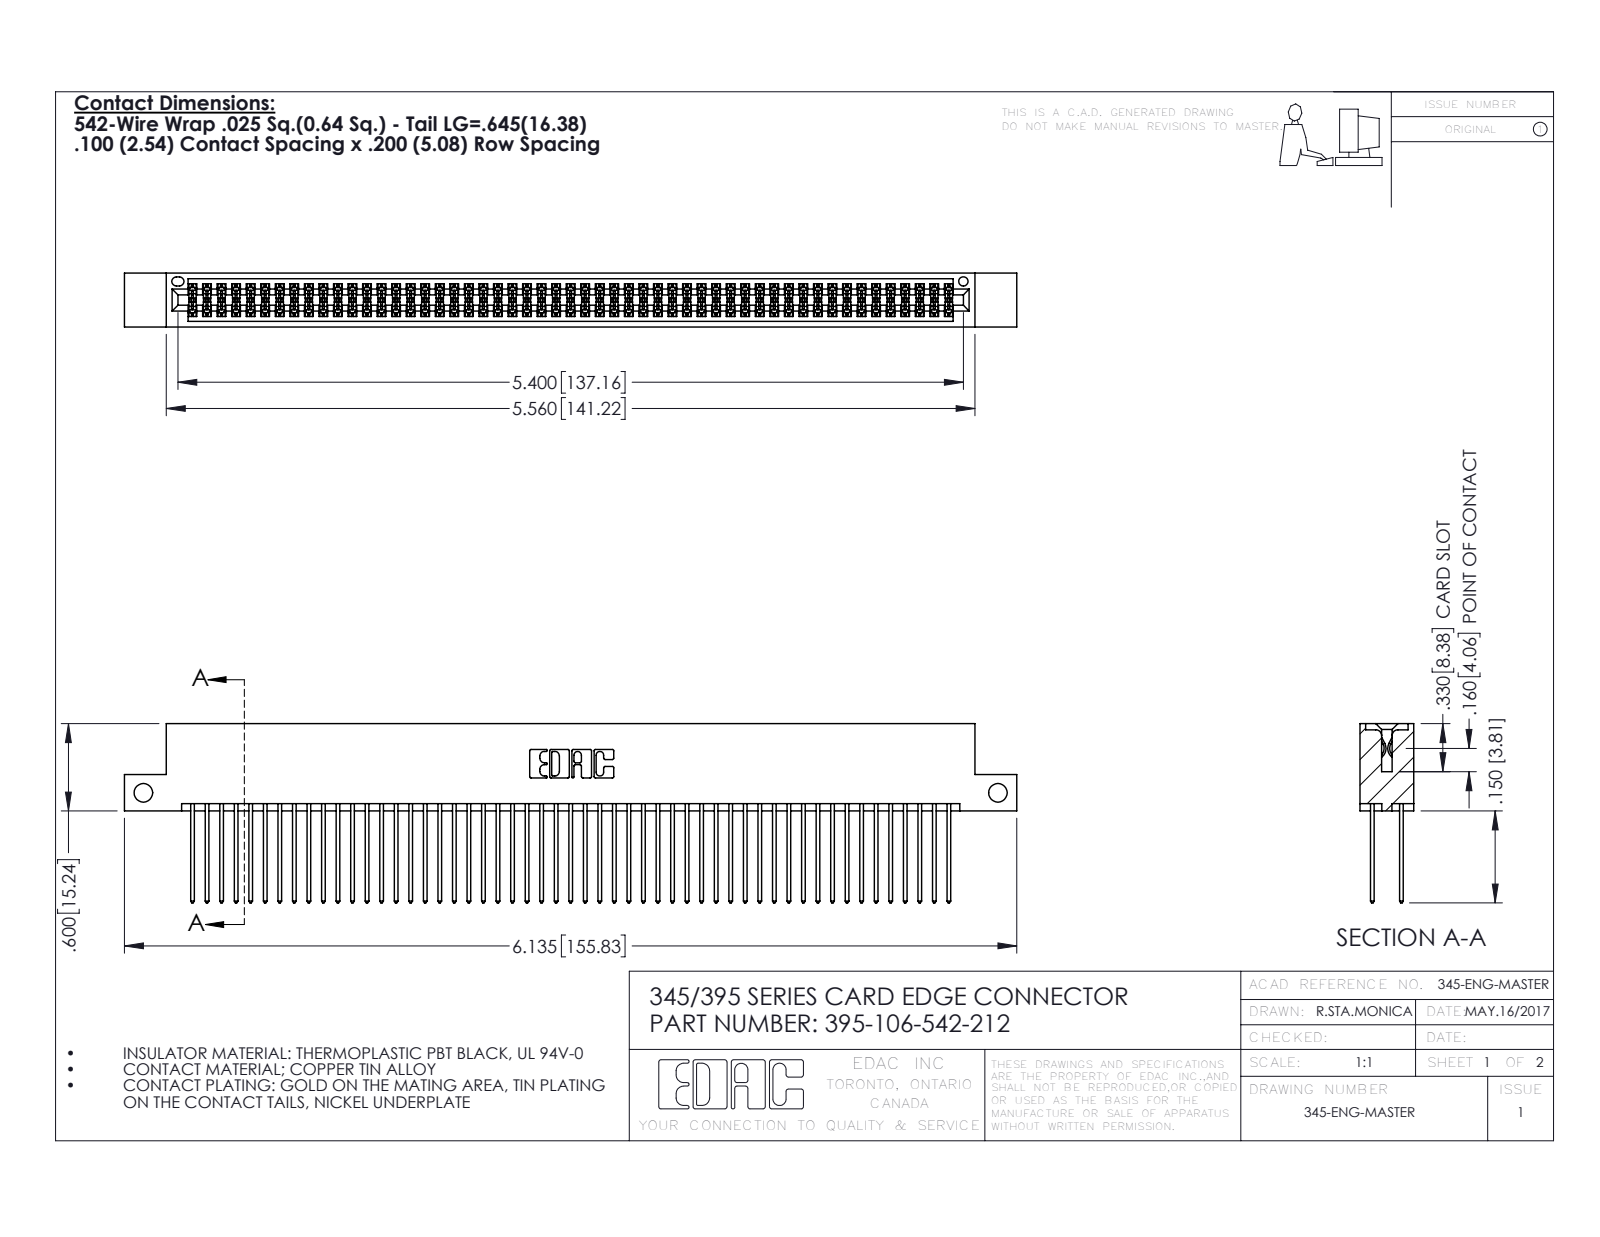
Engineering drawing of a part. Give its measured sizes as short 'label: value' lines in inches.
name: 345-292-001_345-293-142; 395-106-542-212; 345 Part_Flush Mounting Lugs - Side Mount
written by: SolidWorks 2016 (CONFIG_CONTROL_DESIGN)
unit: in
bodies: 107 solids, 5426 faces (3578 planar, 1848 cylindrical, 0 other)
size: 6.135 × 1.232 × 0.37
volume: 0.955 in³; area: 39.55 in²
holes: 2× ⌀0.128, 1× ⌀0.064
rounds: 159× R0.006, 106× R0.01, 22× R0.01, 6× R0.007, 6× R0.031, 3× R0.026, 2× R0.014, 2× R0.019
face distances: 0.298, 0.072, 0.2, 0.098, 0.272, 0.025, 0.225, 0.37, 0.175, 0.149
hole spacings: 5.875
